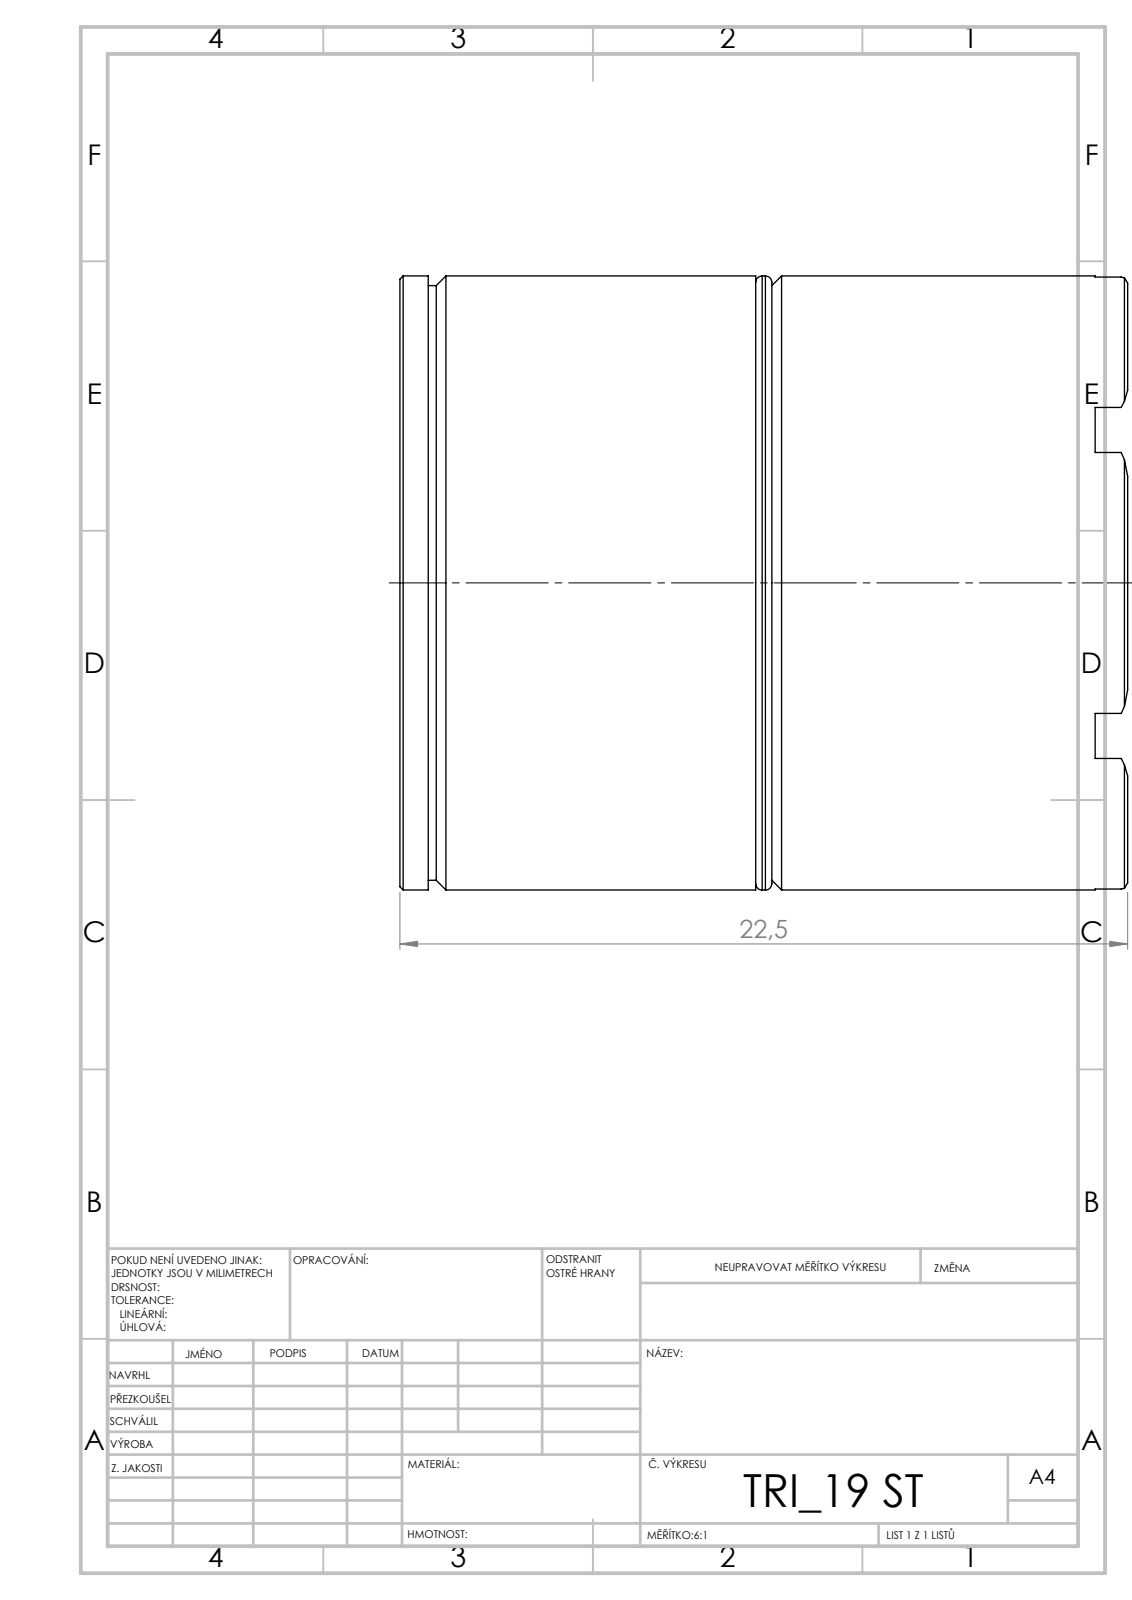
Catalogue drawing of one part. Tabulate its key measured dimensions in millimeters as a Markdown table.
| quantity | value |
| --- | --- |
| STEP written by | SolidWorks 2019 (CONFIG_CONTROL_DESIGN) |
| units | millimeters |
| bodies | 2 solids, 53 faces (24 planar, 12 cylindrical, 17 other) |
| overall size | 22.5 × 19 × 19 |
| volume | 6 246 mm³ |
| surface area | 2 571 mm² |
| round bosses / shafts (diameter × count) | 19 × 1, 18.4 × 1 |
| main face-to-face distances | 11, 11.5, 0.5, 10, 10.5, 21.5, 17.2, 20.63, 10.63, 10.13 |
